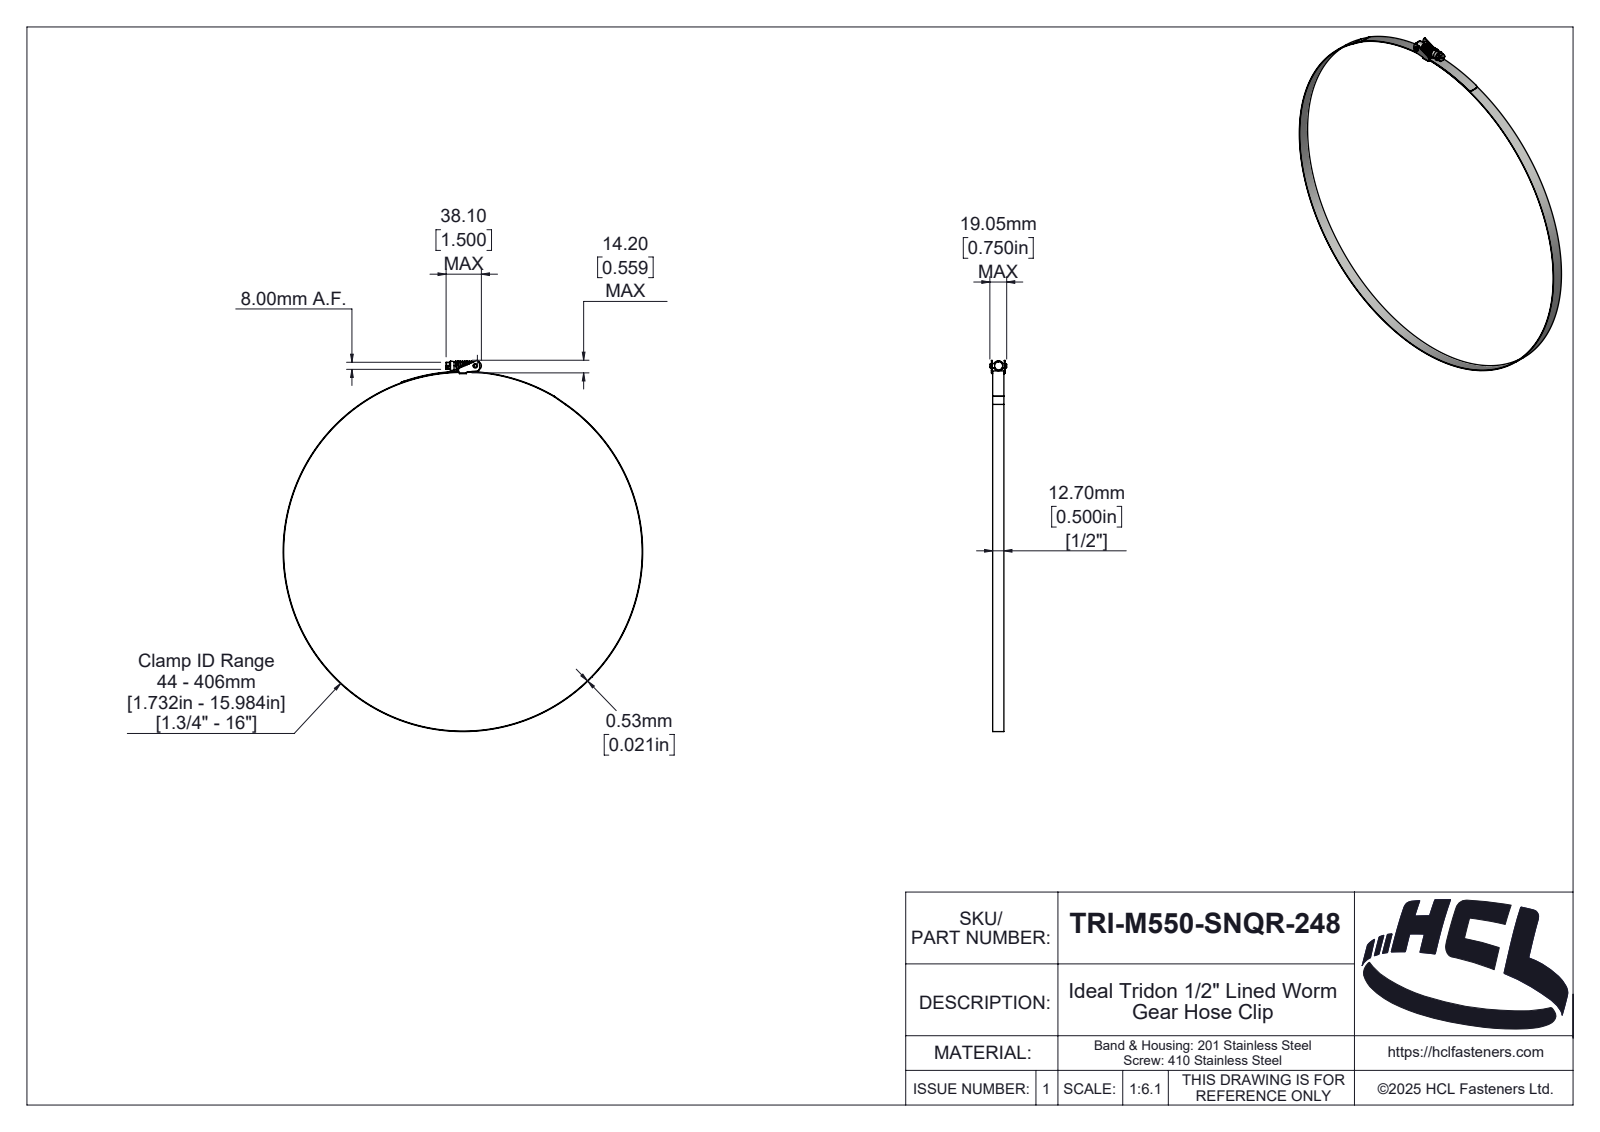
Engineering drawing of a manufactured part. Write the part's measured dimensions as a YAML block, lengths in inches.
part_name: "TRI-M550-SNQR-248"
step_written_by: "SolidWorks 2025 (AUTOMOTIVE_DESIGN)"
units: inches
bodies: {solids: 5, faces: 222, planar: 44, cylindrical: 112, other: 66}
overall_size: [16.536, 16.026, 0.75]
volume: 0.748
surface_area: 60.87
round_holes:
  - {diameter: 0.197, count: 1}
  - {diameter: 15.984, count: 1}
round_bosses_or_shafts:
  - {diameter: 16.026, count: 1}
  - {diameter: 0.358, count: 1}
partial_cylinders:
  - {radius: 0.039, count: 11}
  - {radius: 0.004, count: 2}
  - {radius: 0.035, count: 2}
  - {radius: 0.118, count: 2}
  - {radius: 0.018, count: 1}
  - {radius: 0.074, count: 1}
  - {radius: 0.079, count: 1}
  - {radius: 0.093, count: 1}
face_to_face_distances: [0.5, 0.031, 0.053, 0.553, 0.575, 0.022, 0.522, 0.021, 0.606, 0.543]
hole_center_spacings: [8.302]
